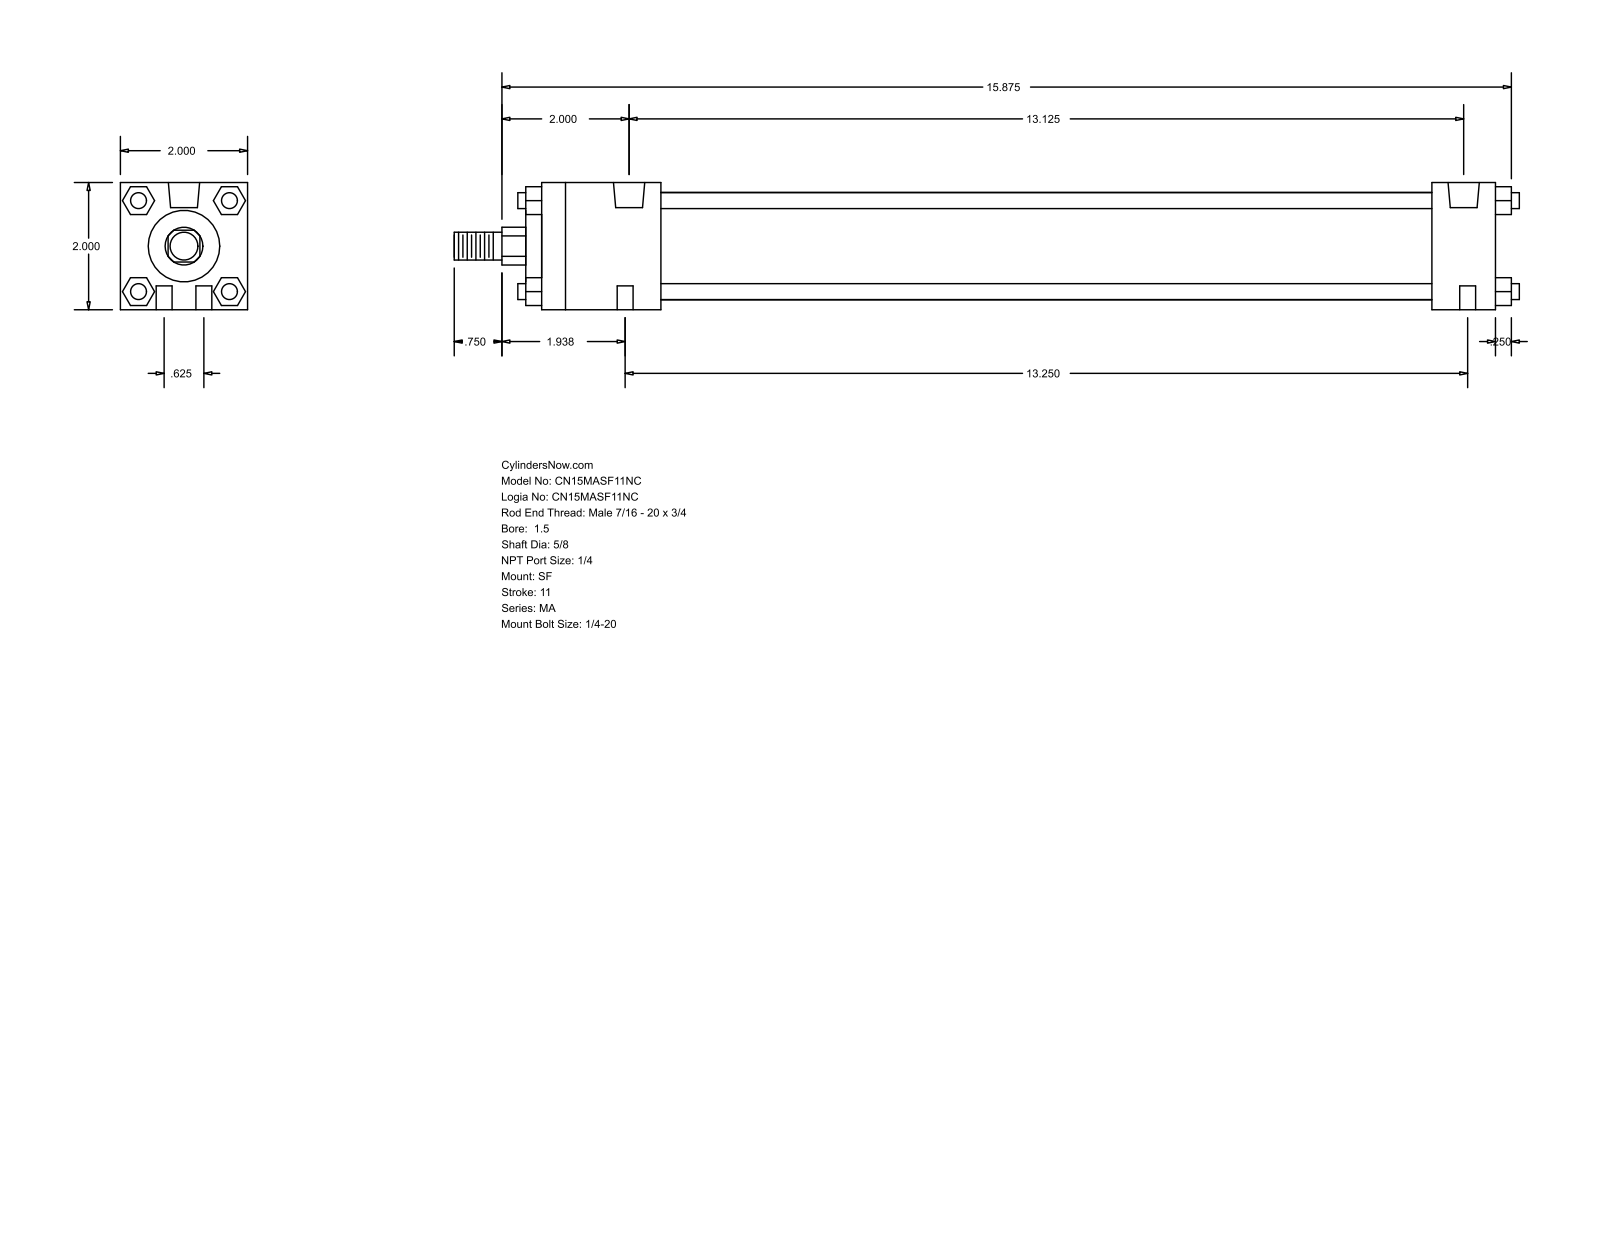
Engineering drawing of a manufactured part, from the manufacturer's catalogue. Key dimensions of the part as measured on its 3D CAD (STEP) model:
Part name (STEP PRODUCT): MA_SF__0150_0.625
STEP written by: GSSL Pune (CONFIG_CONTROL_DESIGN)
Units: millimetres
Bodies: 0 solids, 124 faces (94 planar, 30 cylindrical, 0 other)
Overall size (bounding box): 425.45 × 50.8 × 50.8
Round holes (diameter × count): ⌀6.35 ×4, ⌀7.94 ×2, ⌀12.49 ×2
Round bosses / shafts (diameter × count): ⌀6.35 ×4, ⌀42.93 ×1, ⌀28.57 ×1, ⌀15.88 ×1, ⌀11.11 ×1
Partial cylindrical surfaces — rounded edges, fillets, slot ends (radius × count): R7.54 ×1
Main face-to-face distances: 50.8, 381, 6.35, 25.4, 387.35, 47.62, 355.6, 307.98, 333.38, 53.97
Hole centre spacings: 8.1, 15.88, 333.38, 335.05, 335.06, 336.55, 336.92
